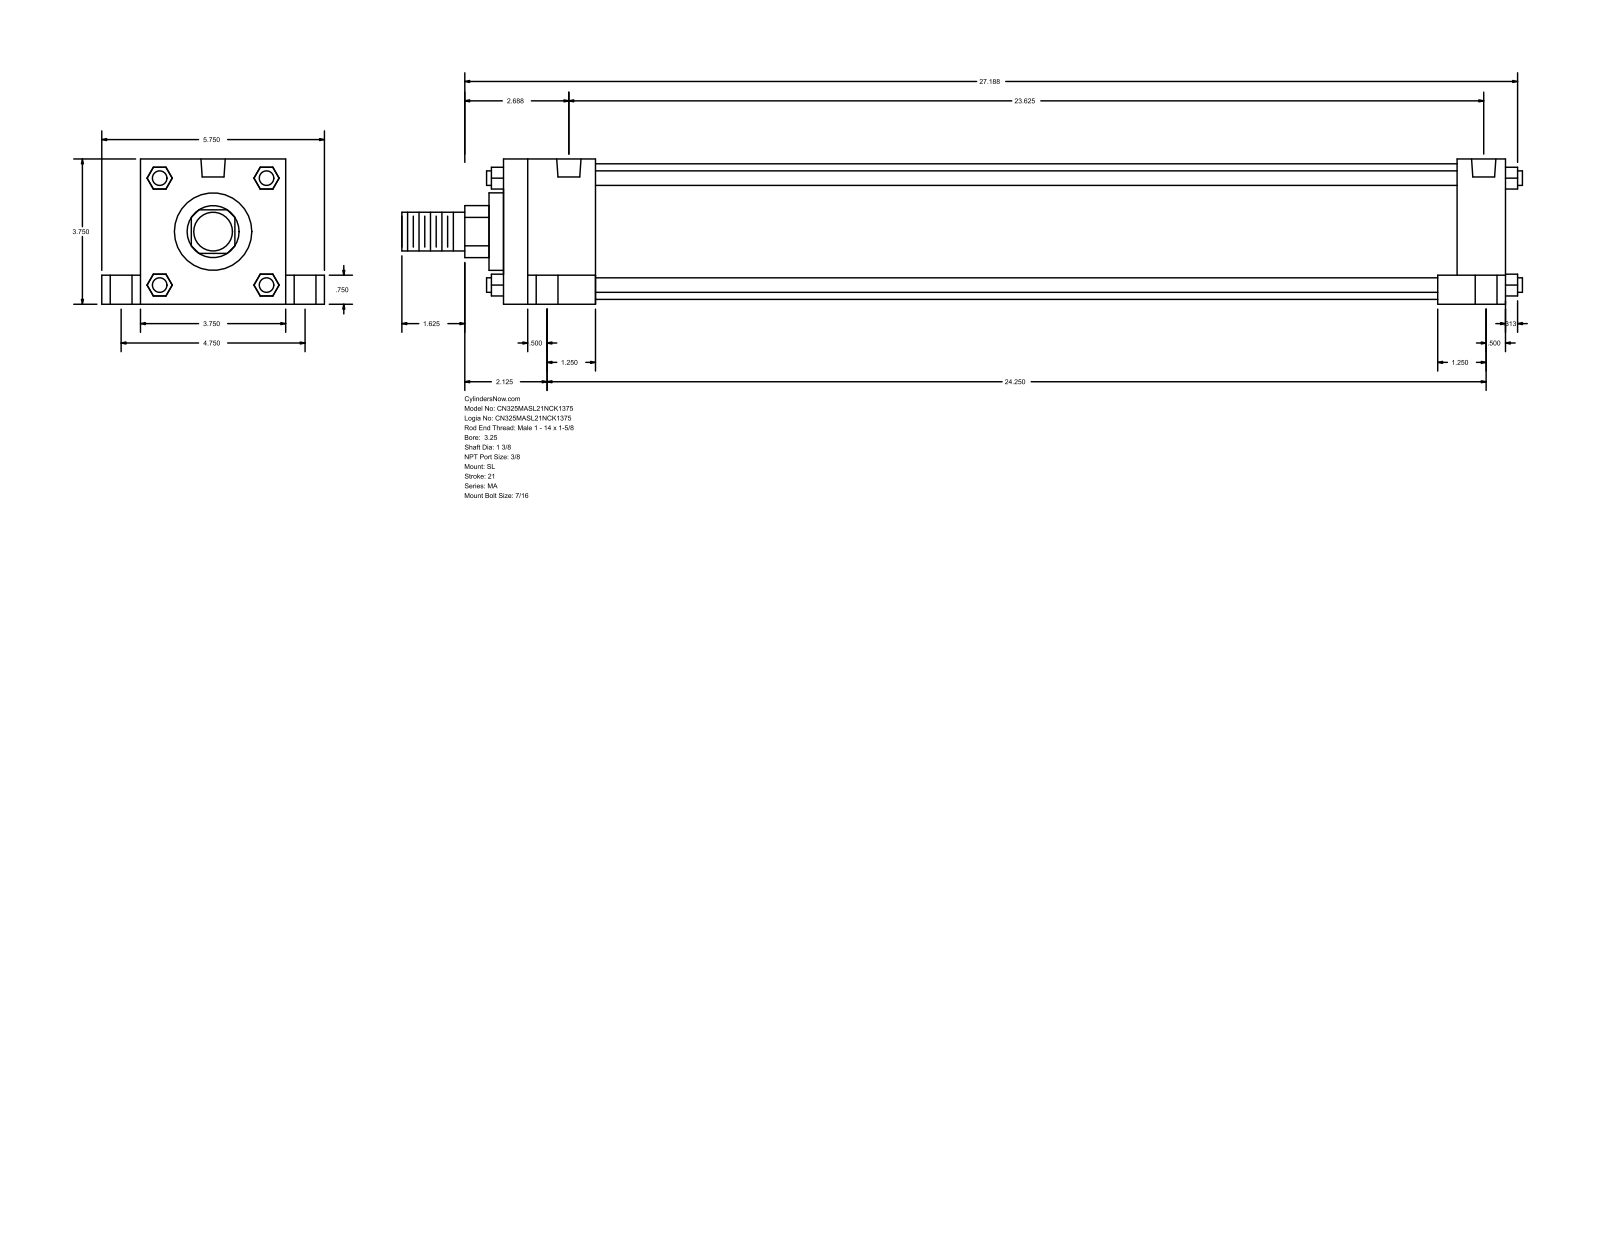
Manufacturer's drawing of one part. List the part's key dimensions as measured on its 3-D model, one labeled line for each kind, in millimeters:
Part name (STEP PRODUCT): MA_SL__0325_1.375
STEP written by: GSSL Pune (CONFIG_CONTROL_DESIGN)
Units: millimetres
Bodies: 0 solids, 148 faces (112 planar, 36 cylindrical, 0 other)
Overall size (bounding box): 735.01 × 146.05 × 95.25
Round holes (diameter × count): ⌀11.11 ×4, ⌀14.29 ×4, ⌀20.64 ×4, ⌀15.93 ×2
Round bosses / shafts (diameter × count): ⌀9.53 ×4, ⌀88.9 ×1, ⌀50.8 ×1, ⌀34.92 ×1, ⌀25.4 ×1
Partial cylindrical surfaces — rounded edges, fillets, slot ends (radius × count): R17.06 ×1
Main face-to-face distances: 95.24, 657.22, 25.41, 120.65, 625.48, 31.74, 60.32, 565.16, 596.9, 19.05
Hole centre spacings: 60.35, 60.66, 62, 63.27, 120.66, 590.55, 599.93, 604.68
